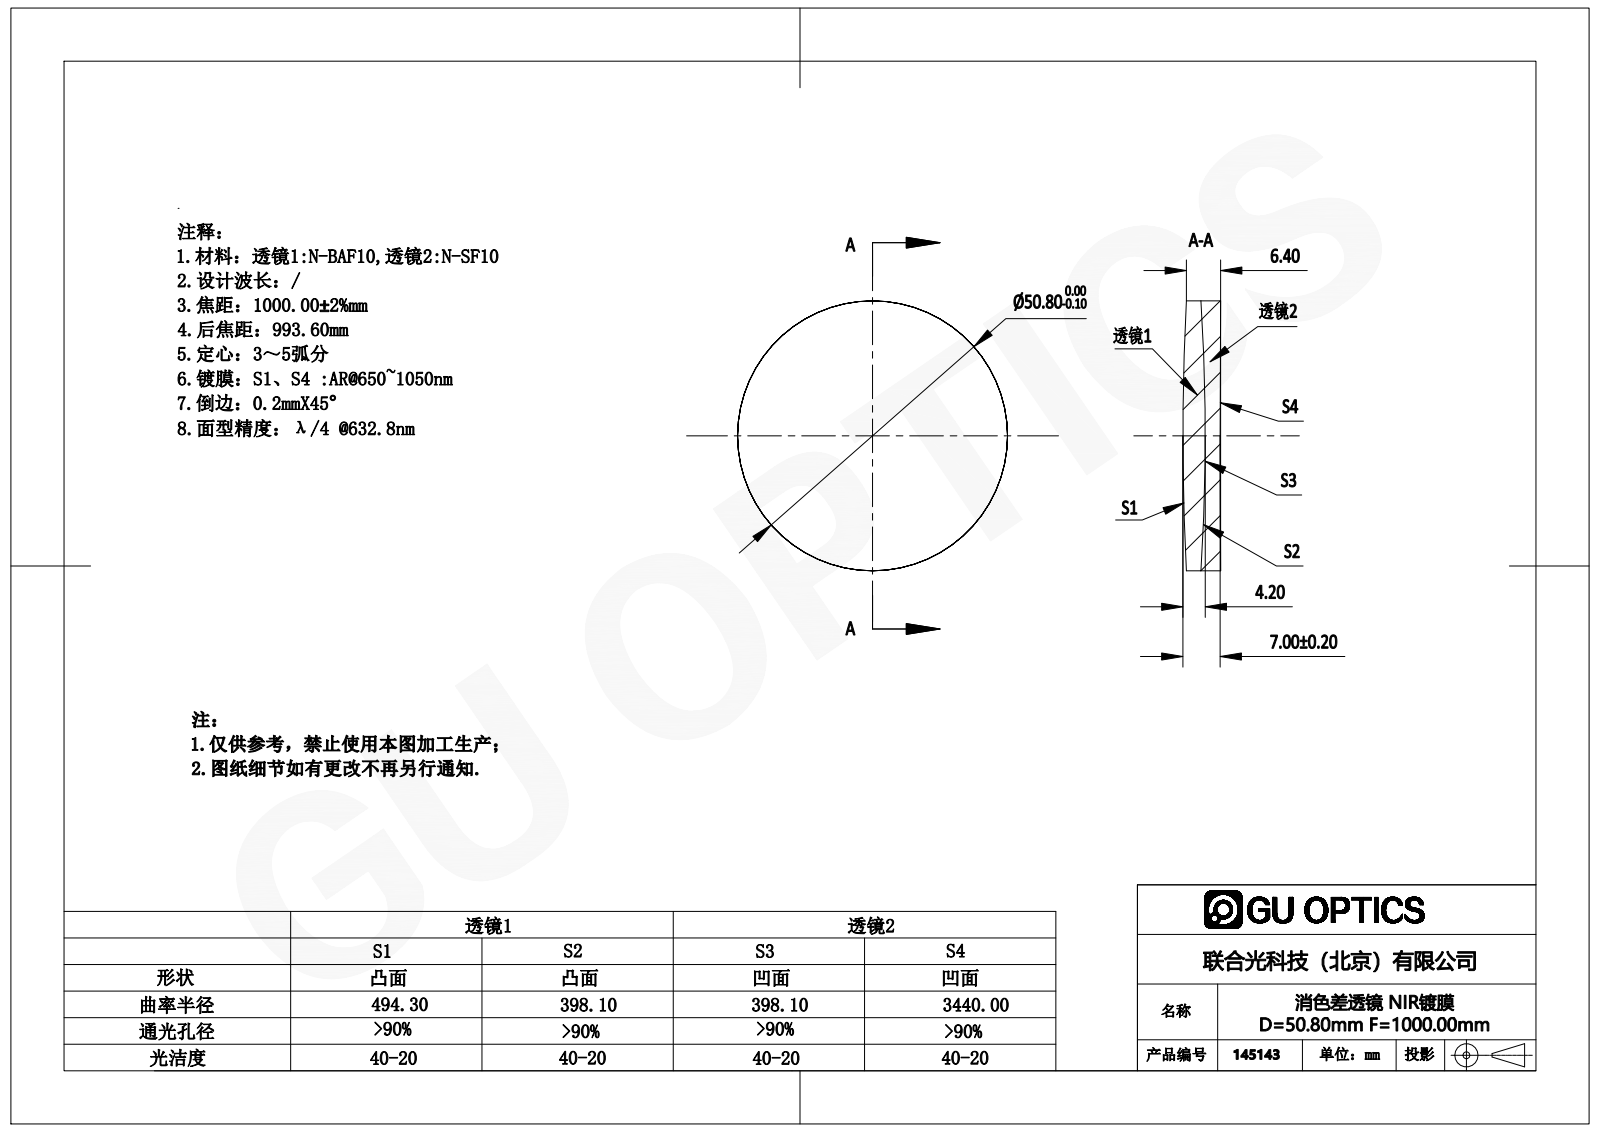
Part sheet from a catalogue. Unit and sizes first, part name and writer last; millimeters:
Units: millimetres
Overall size (bounding box): 50.8 × 50.8 × 7.09
Round bosses / shafts (diameter × count): ⌀50.8 ×1
Volume: 13 621 mm³ · Surface area: 9 141 mm²
Bodies: 2 solids, 12 faces (0 planar, 4 cylindrical, 8 other)
Part name (STEP PRODUCT): 145143
STEP written by: SolidWorks 2016 (AUTOMOTIVE_DESIGN)
